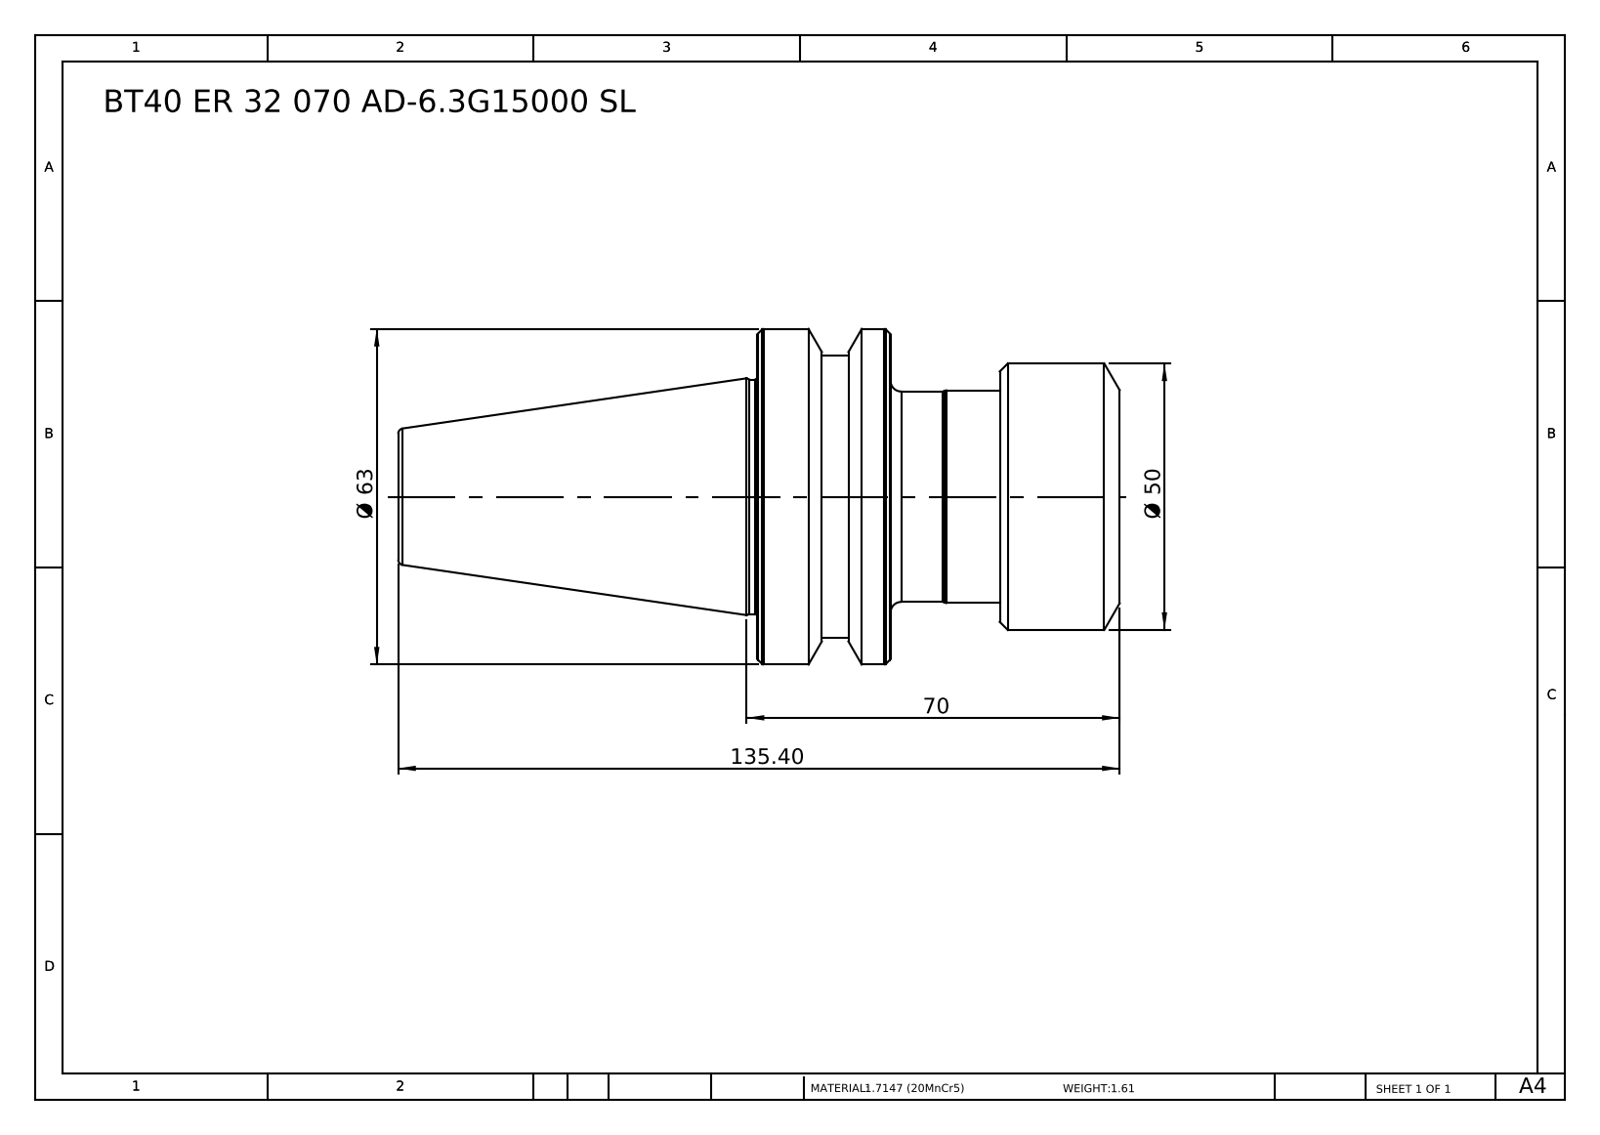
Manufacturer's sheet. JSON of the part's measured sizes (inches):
{"part_name": "BT40 ER 32 070 AD-6.3G15000 SL", "step_written_by": "SolidWorks 2014 (CONFIG_CONTROL_DESIGN)", "units": "inches", "bodies": {"solids": 1, "faces": 55, "planar": 7, "cylindrical": 14, "other": 34}, "overall_size": [5.331, 2.48, 2.48], "volume_in3": 12.62, "surface_area_in2": 39.18, "round_bosses_or_shafts": [[2.48, 1], [2.087, 1], [1.969, 1], [1.732, 1], [1.571, 1], [1.555, 1]], "face_to_face_distances": [0.984, 1.693, 2.677, 0.886, 0.807, 1.791, 5.331, 4.445, 3.638, 2.654]}
